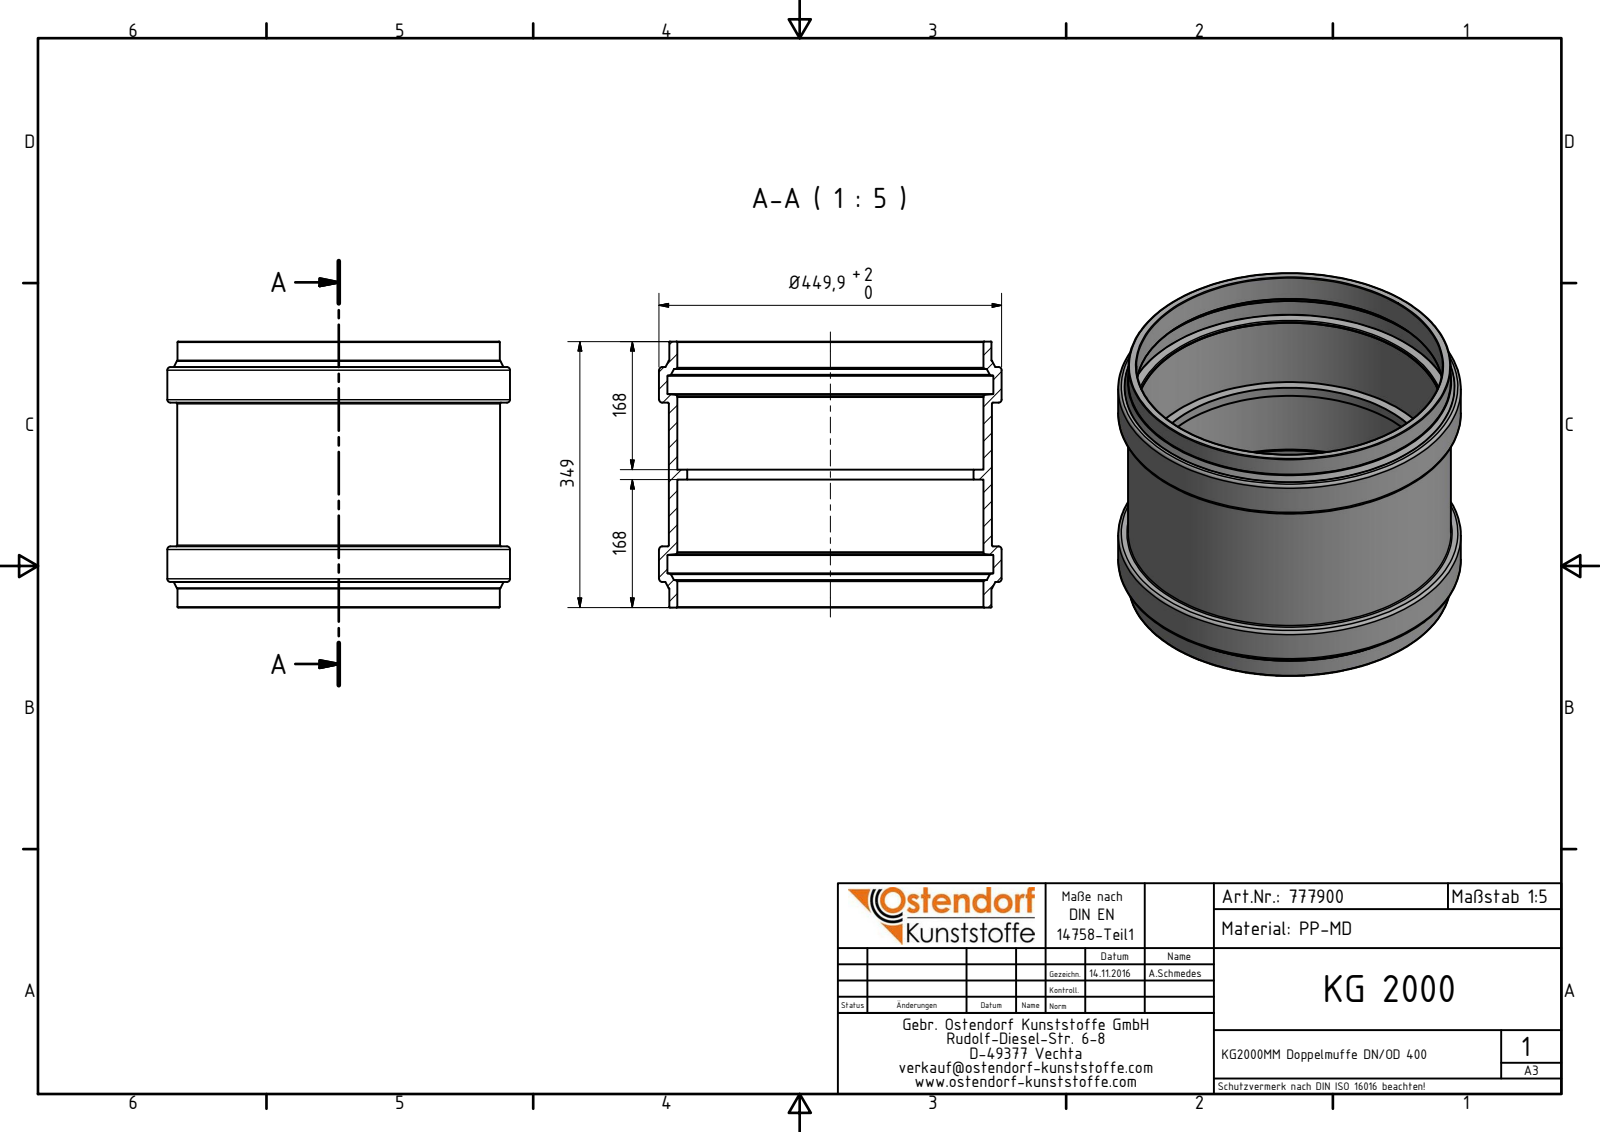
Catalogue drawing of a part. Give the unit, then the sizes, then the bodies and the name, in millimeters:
Units: millimetres
Overall size (bounding box): 449.9 × 449.9 × 349
Round holes (diameter × count): ⌀376 ×1, ⌀401.7 ×1, ⌀402.1 ×1, ⌀427.7 ×1
Round bosses / shafts (diameter × count): ⌀449.9 ×1, ⌀423.9 ×1, ⌀423.06 ×1
Main face-to-face distances: 168, 181, 80.2, 268.8, 87.8, 100.8, 13, 33.6, 315.4, 46.6
Volume: 5 876 000 mm³ · Surface area: 1 074 000 mm²
Bodies: 1 solid, 62 faces (10 planar, 14 cylindrical, 38 other)
Part name (STEP PRODUCT): 777900 KG2000MM Doppelmuffe DN_OD 400
STEP written by: Autodesk Inventor 2016 (AUTOMOTIVE_DESIGN)
